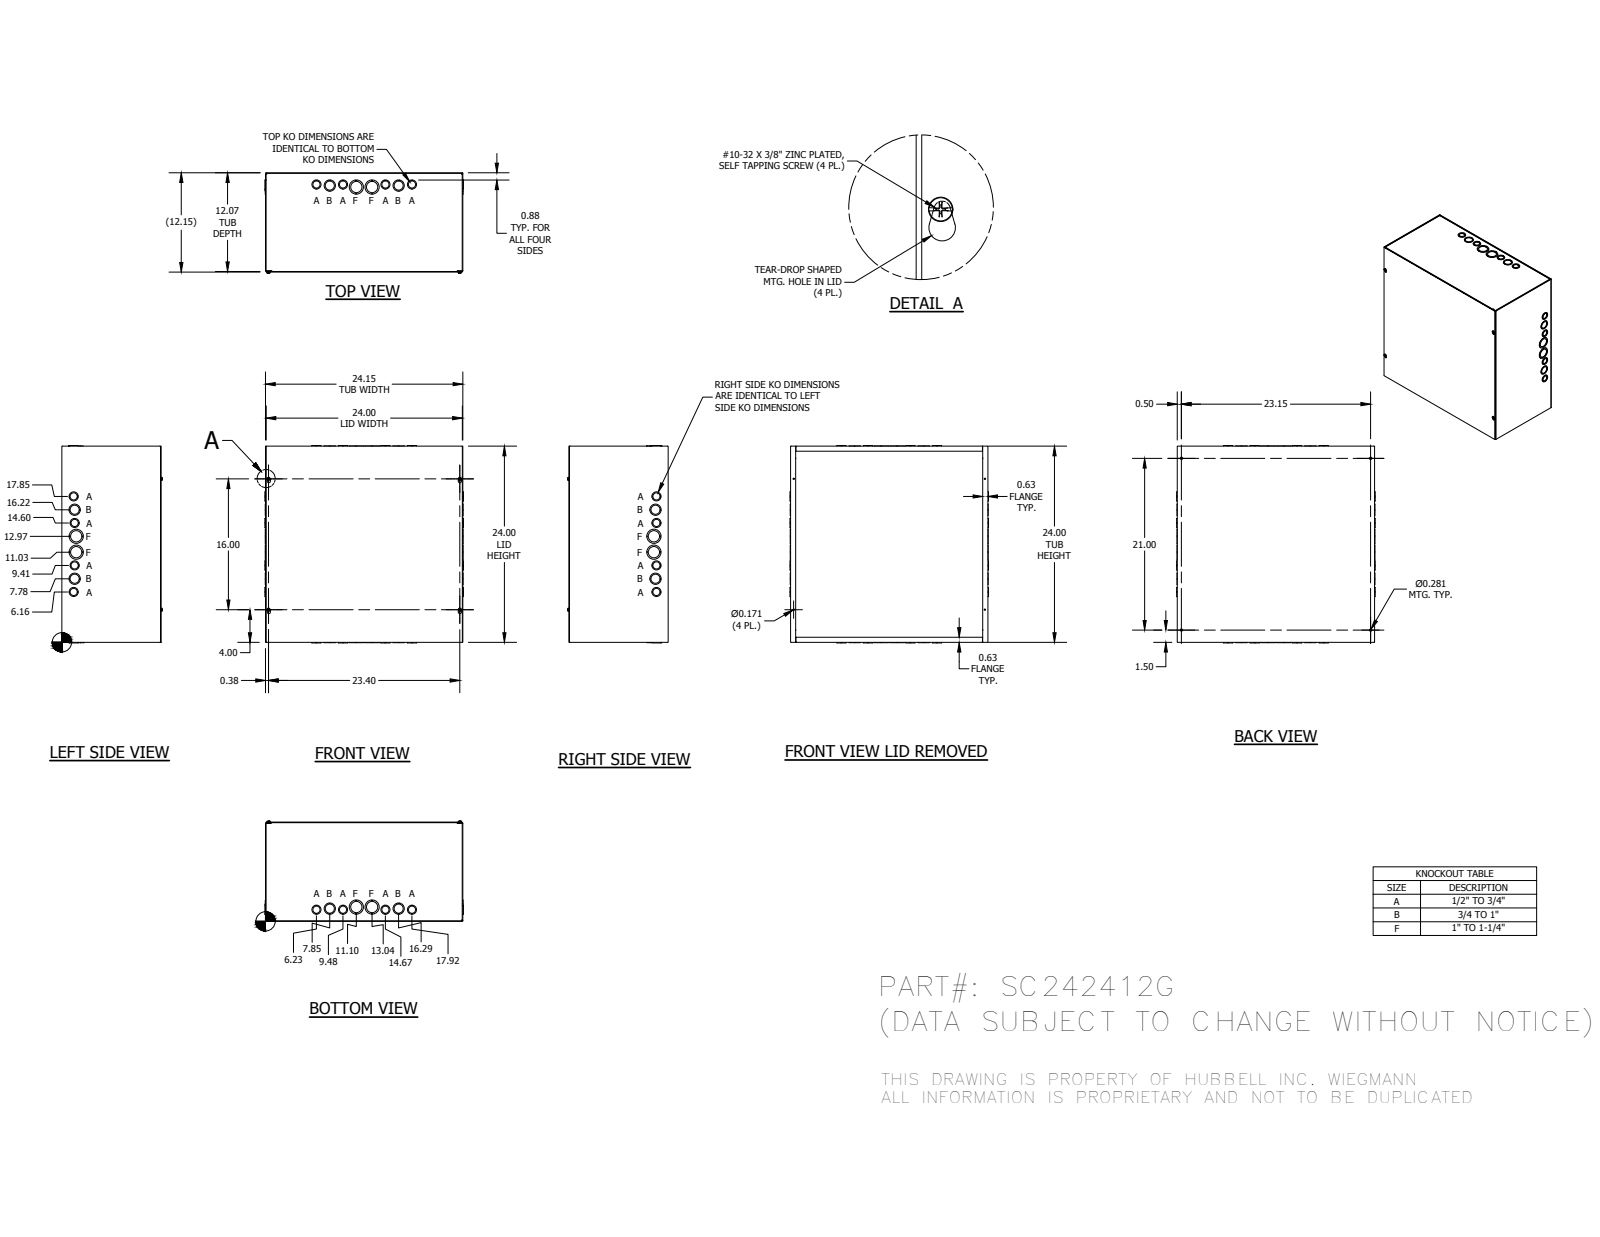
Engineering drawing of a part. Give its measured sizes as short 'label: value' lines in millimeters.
name: SC242412GBLR; SC2412GTB; SC2424GLPA; 37214 (+1 more)
written by: Autodesk Inventor 2014 (AUTOMOTIVE_DESIGN)
unit: mm
bodies: 37 solids, 1219 faces (899 planar, 236 cylindrical, 84 other)
size: 617.12 × 613.36 × 311.91
holes: 14× ⌀28.57, 10× ⌀22.22, 8× ⌀34.92, 4× ⌀4.34, 4× ⌀7.14, 4× ⌀44.45
bosses: 4× ⌀4.83
rounds: 12× R0.4, 12× R2.28, 4× R3.17, 4× R5.16
face distances: 1.88, 306.68, 304.8, 609.6, 607.72, 611.48, 308.56, 613.36, 605.84, 3.76
hole spacings: 41.39, 41.4, 42.03, 63.58, 82.55, 82.69, 90.9, 124.07
